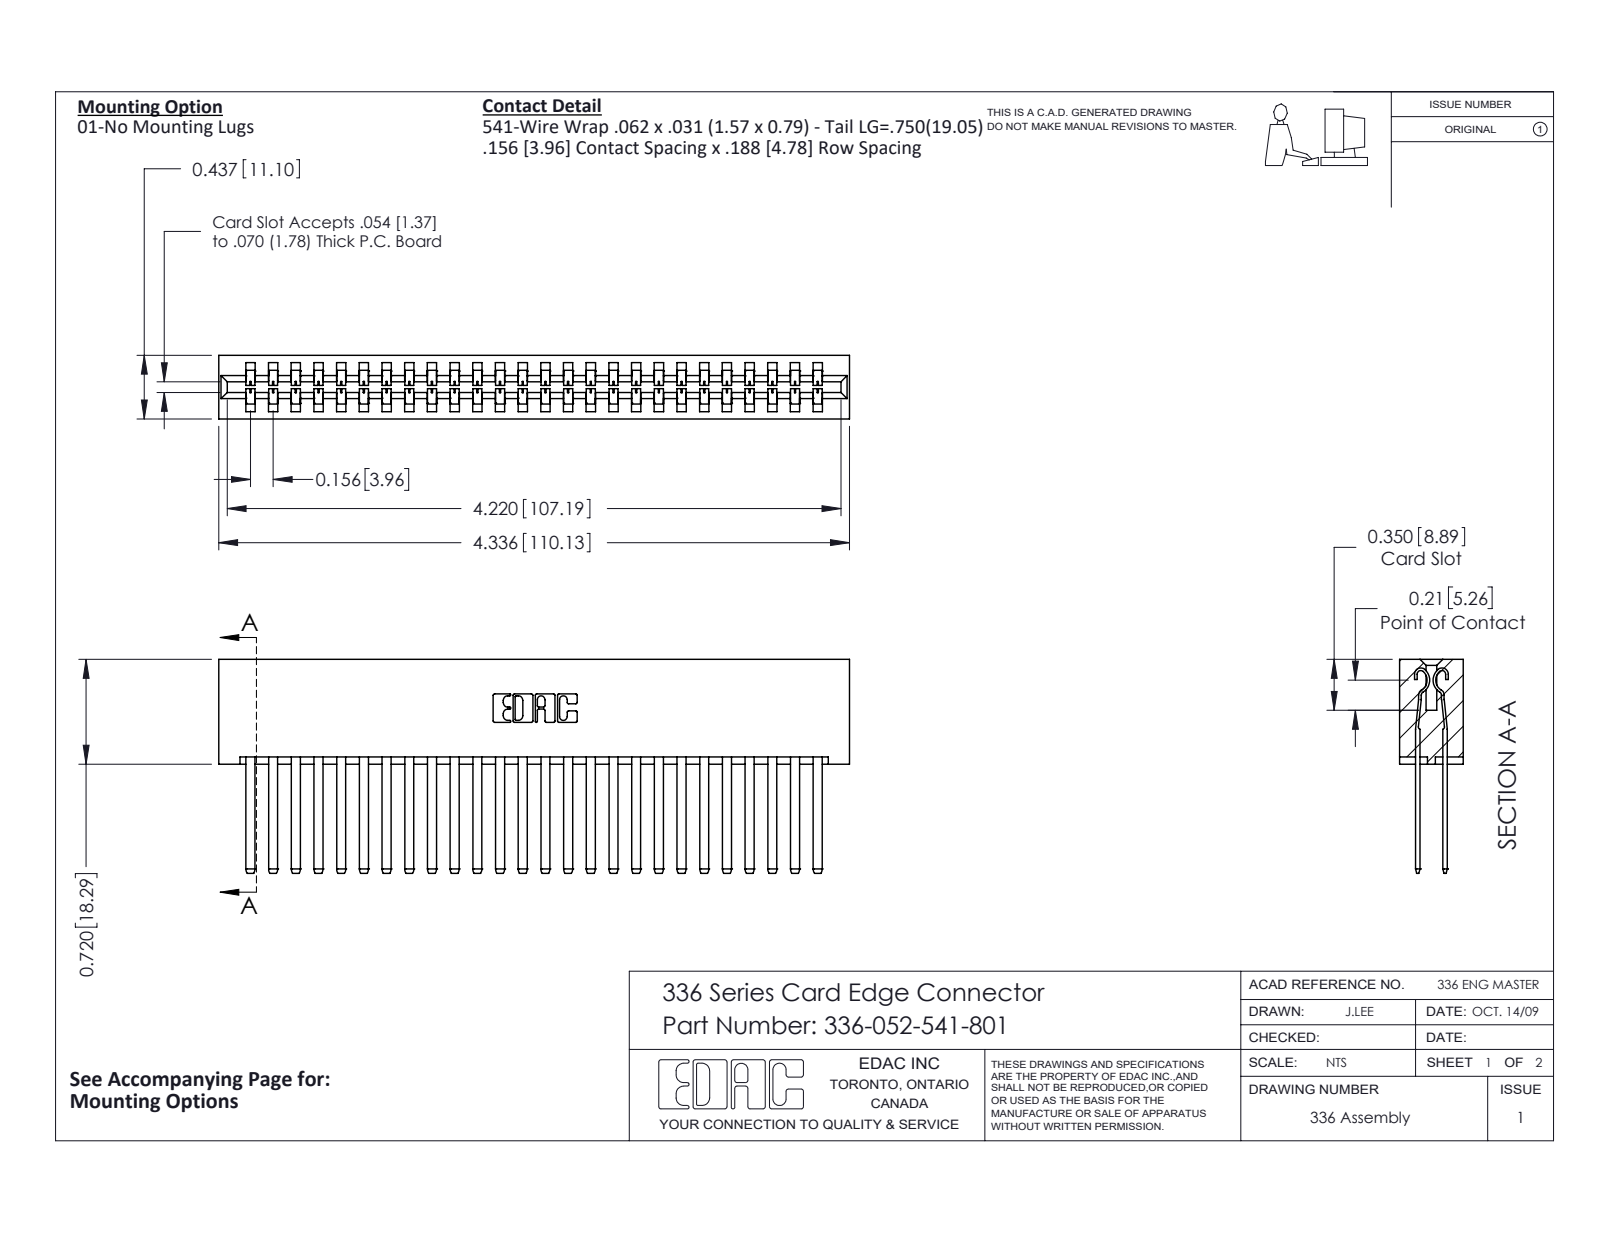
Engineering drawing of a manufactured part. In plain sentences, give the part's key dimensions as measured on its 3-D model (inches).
The part is named "336-052-541-801; 336 Part_Lugless; 336-290-001_336-290-541". Its 3-D file was written by "SolidWorks 2020 (CONFIG_CONTROL_DESIGN)". It is 53 solids with 2290 faces: 1418 planar, 872 cylindrical and 0 other. Overall it measures 4.336 by 1.47 by 0.437 inches. Its volume is 1.109 cubic inches and its surface area 35.84 square inches. Partial cylindrical surfaces (rounded edges, fillets, slot ends): 104 of radius 0.004, 52 of radius 0.056, 22 of radius 0.01, 6 of radius 0.007, 6 of radius 0.031, 4 of radius 0.022, 4 of radius 0.04, 3 of radius 0.026. The main face-to-face distances are 0.188, 0.328, 0.14, 0.297, 0.109, 0.031, 0.437, 0.033, 0.181, 0.256.
